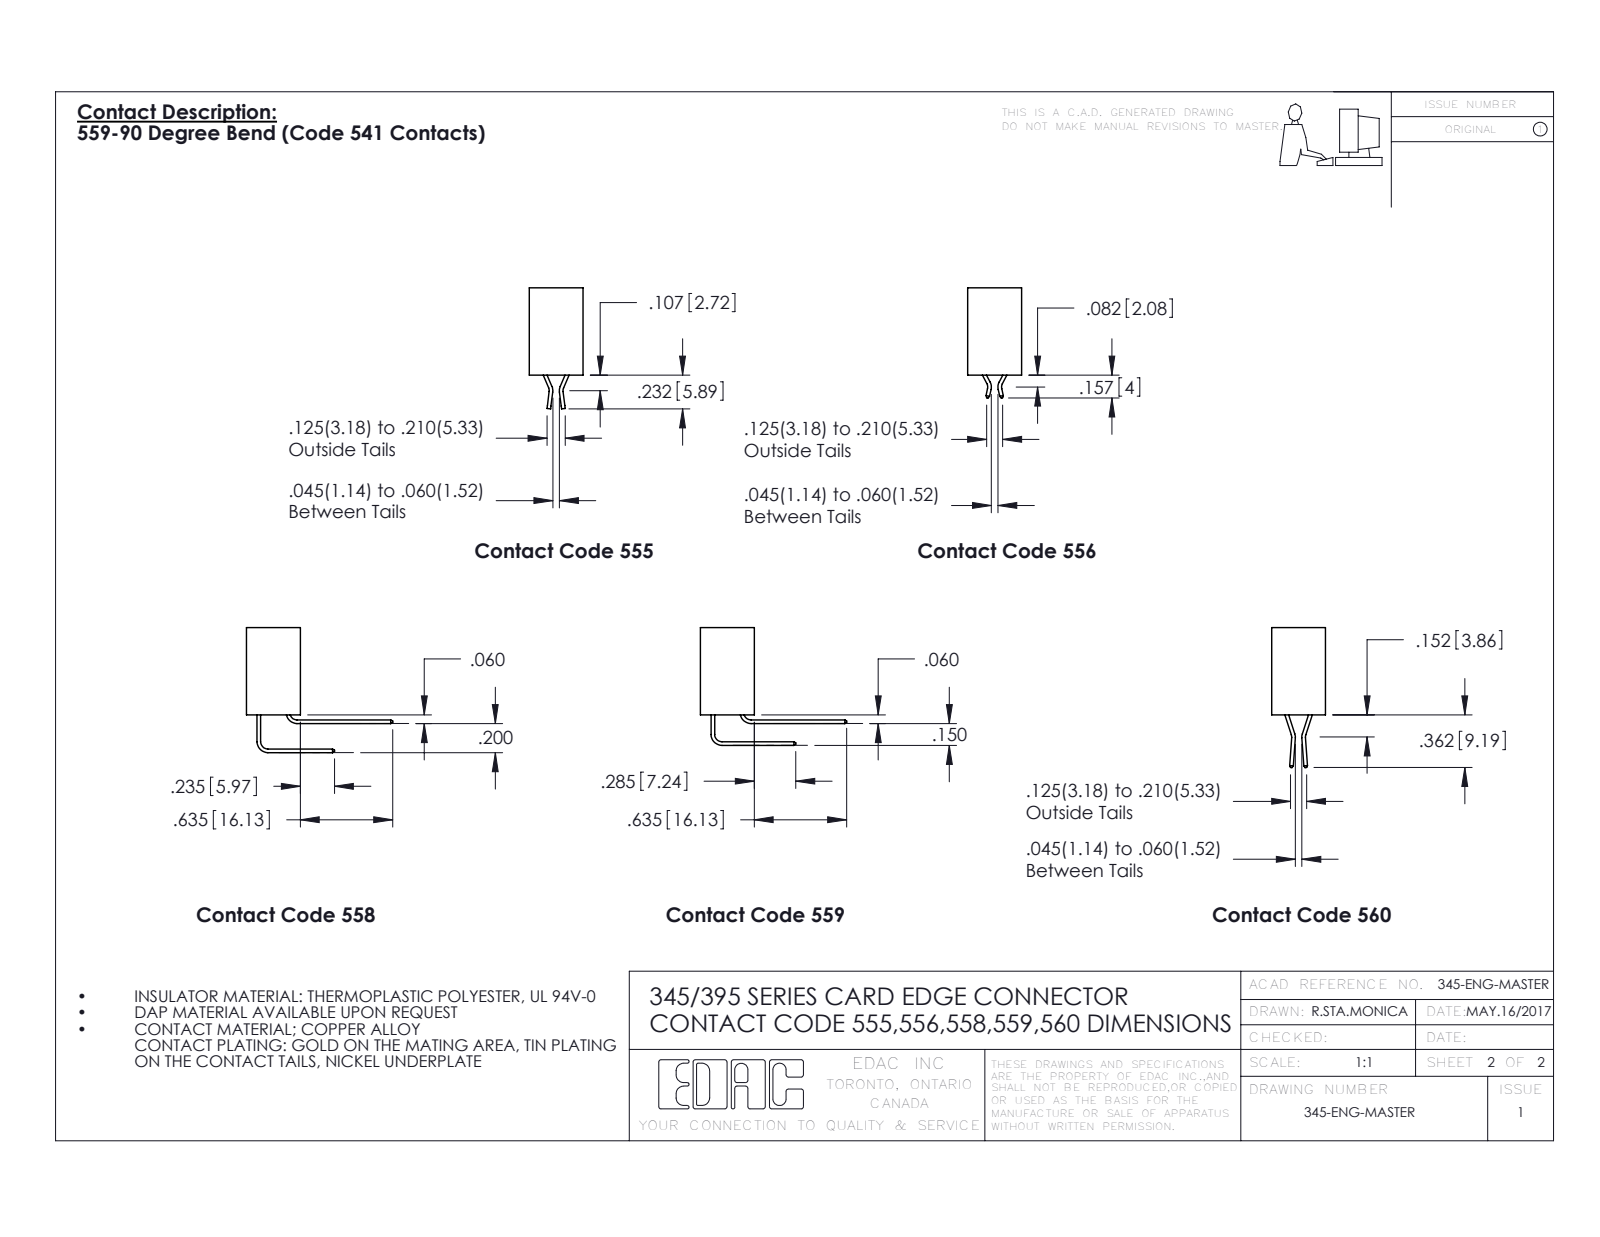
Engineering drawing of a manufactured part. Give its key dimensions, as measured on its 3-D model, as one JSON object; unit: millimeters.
{"part_name": "395-056-559-201; 345-292-001_559 Tail - 2; 345-292-001_558 559 Tail - 1; 345 Part_No Mounting Lugs", "step_written_by": "SolidWorks 2016 (CONFIG_CONTROL_DESIGN)", "units": "millimeters", "bodies": {"solids": 57, "faces": 3030, "planar": 2036, "cylindrical": 994, "other": 0}, "overall_size": [77.7, 25.5, 20.5], "volume_mm3": 8360, "surface_area_mm2": 13910, "round_holes": [[1.6, 1]], "partial_cylinders_radius": [[0.2, 112], [0.3, 22], [0.2, 6], [0.8, 6], [0.7, 3], [0.4, 2], [0.5, 2], [0.6, 2]], "face_to_face_distances": [1.8, 7.6, 5.1, 9.4, 2.5, 6.9, 0.6, 5.7, 3.8, 4.4]}
